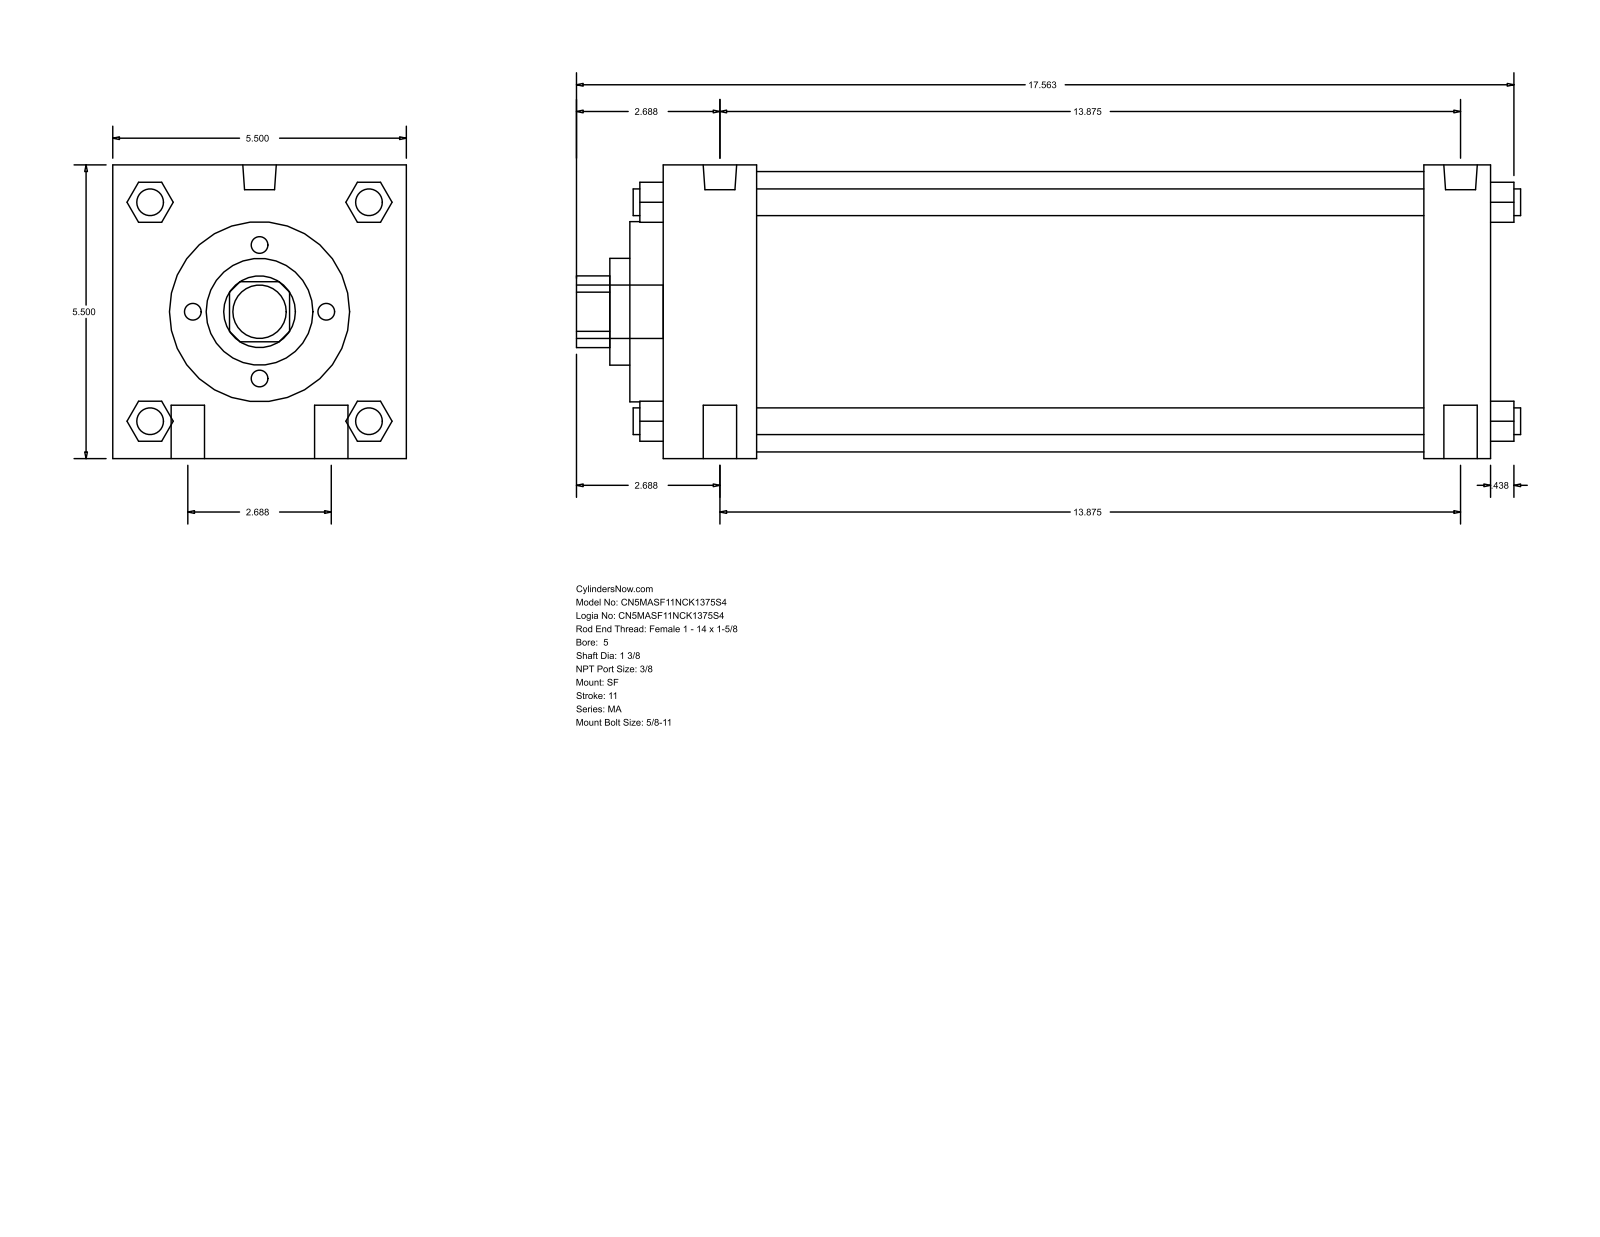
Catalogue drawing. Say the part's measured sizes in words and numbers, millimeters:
The part is named "MA_SF__0500_1.375". Its 3-D file was written by "GSSL Pune (CONFIG_CONTROL_DESIGN)". It is 0 solids with 126 faces: 95 planar, 31 cylindrical and 0 other. Overall it measures 449.26 by 139.7 by 139.7 millimeters. Round holes: 1 of diameter 34.92, 1 of diameter 50.8, 1 of diameter 85.72, 1 of diameter 133.35. Round bosses or shafts: 4 of diameter 15.88, 4 of diameter 12.7, 2 of diameter 15.93, 2 of diameter 11.11, 1 of diameter 25.4. Partial cylindrical surfaces (rounded edges, fillets, slot ends): 1 of radius 17.06. The main face-to-face distances are 139.7, 393.71, 44.45, 361.96, 317.51, 349.26, 31.75, 15.87, 60.32, 377.83.
